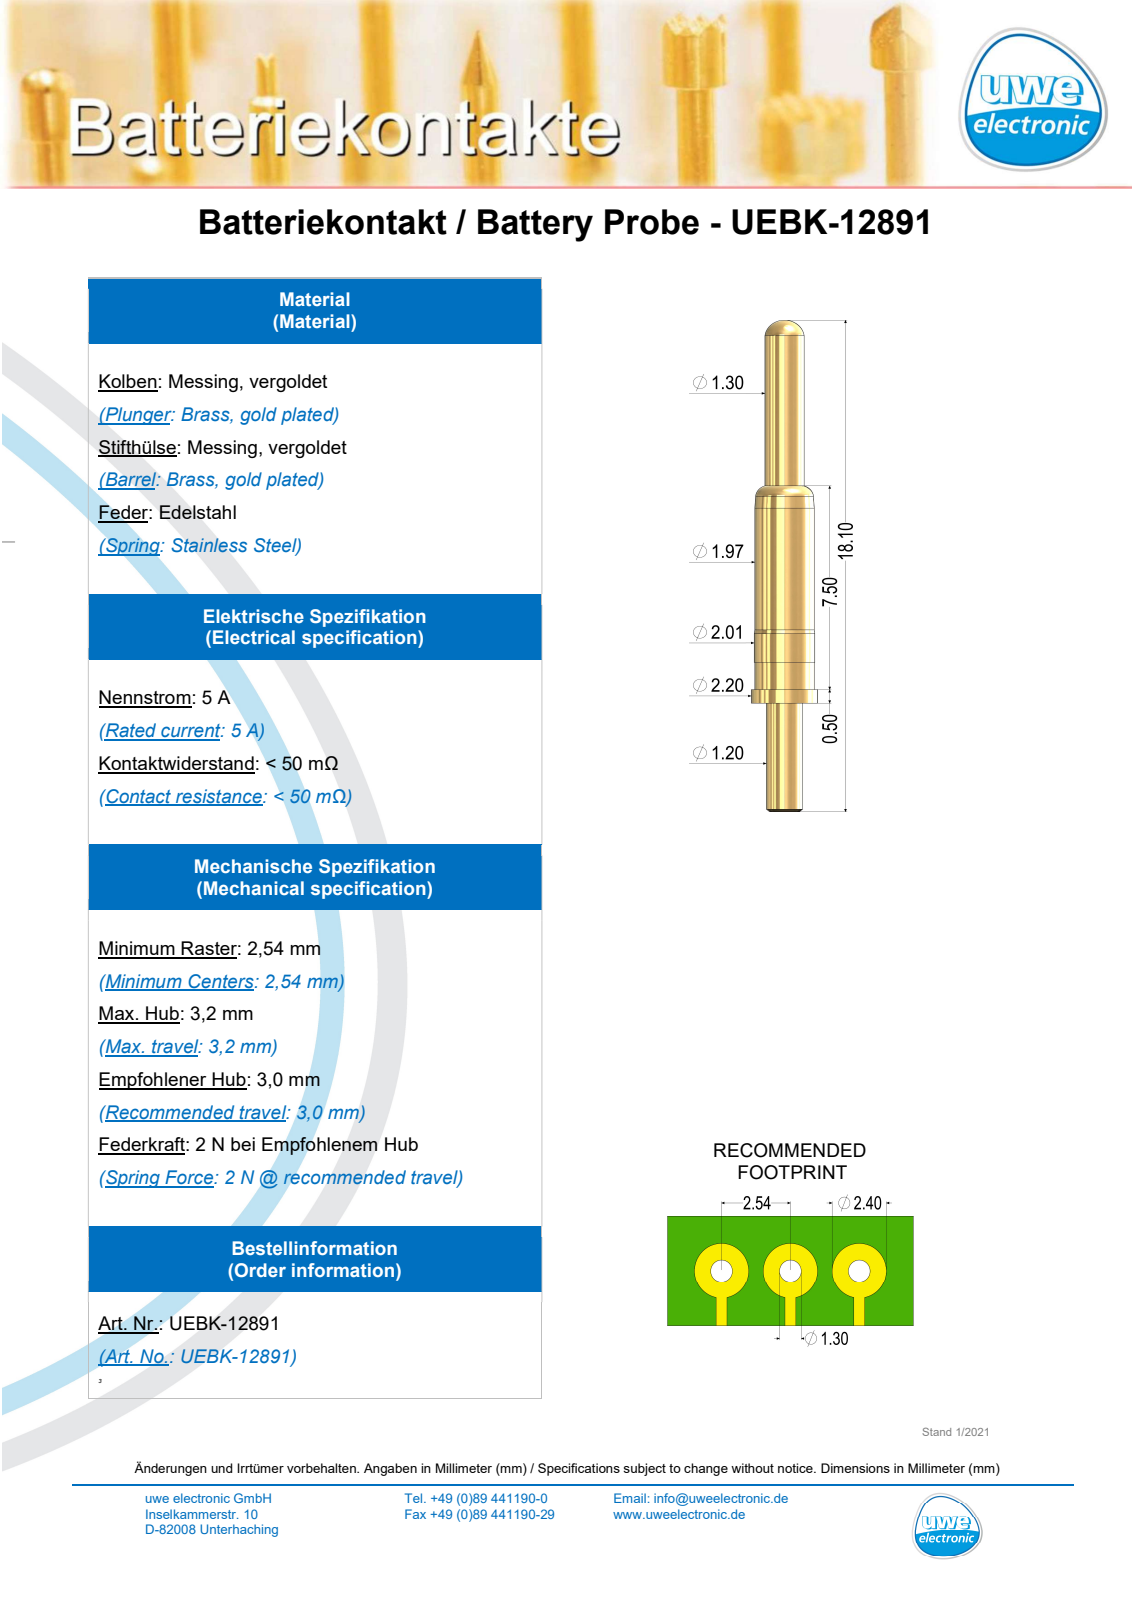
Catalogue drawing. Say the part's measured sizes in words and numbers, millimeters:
The part is named "UEBK-12891_2017_09_05". Its 3-D file was written by "SolidWorks 2017 (AUTOMOTIVE_DESIGN)". It is 1 solid with 26 faces: 4 planar, 12 cylindrical and 10 other. Overall it measures 18.1 by 2.2 by 2.2 millimeters. Its volume is 37 cubic millimeters and its surface area 95 square millimeters. Round bosses or shafts: 1 of diameter 2.2, 1 of diameter 2.01, 1 of diameter 1.97, 1 of diameter 1.3, 1 of diameter 1.2. The main face-to-face distances are 4, 4.5, 0.5, 5.5, 1.5, 1.
